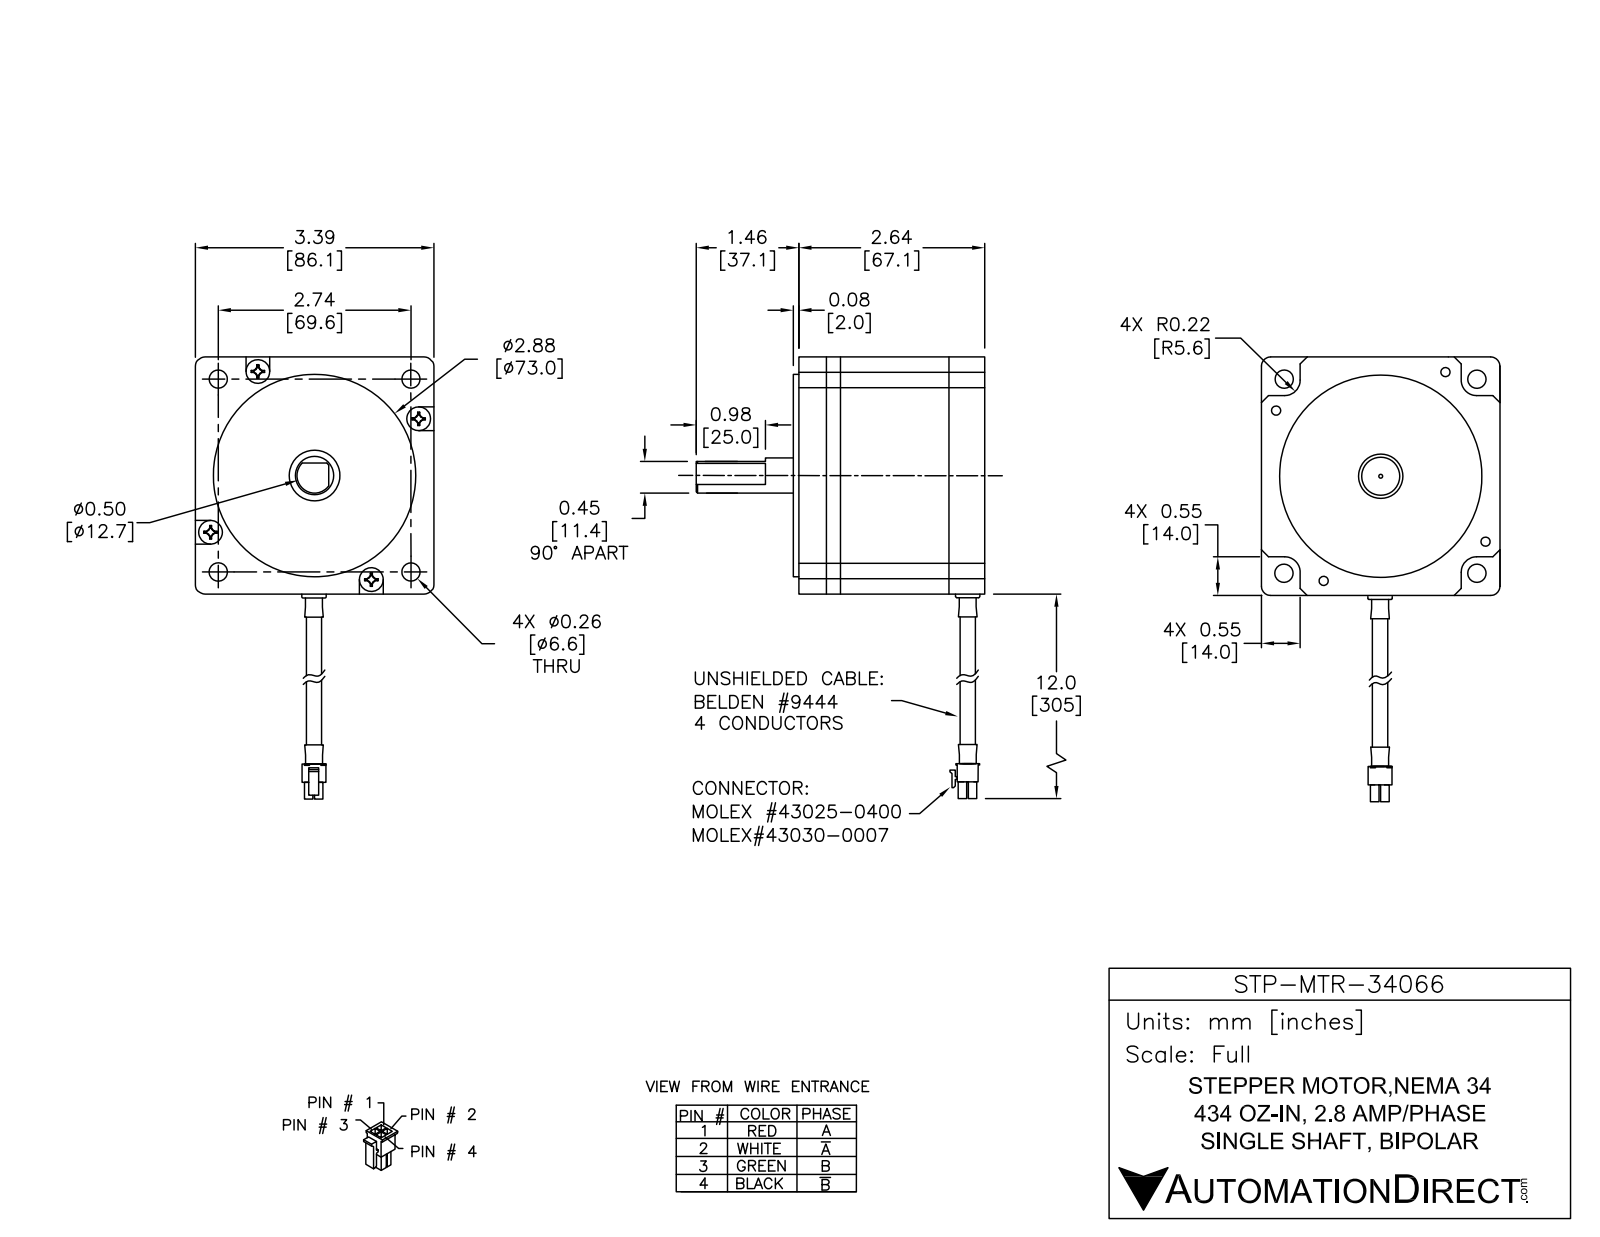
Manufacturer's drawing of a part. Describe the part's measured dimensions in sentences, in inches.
The part is named "STP-MTR-34066". Its 3-D file was written by "SolidWorks 2014 (AUTOMOTIVE_DESIGN)". It is 1 solid with 67 faces: 28 planar, 36 cylindrical and 3 other. Overall it measures 6.185 by 4.06 by 3.37 inches. Its volume is 27.1 cubic inches and its surface area 61.46 square inches. Round holes: 4 of diameter 0.26. Round bosses or shafts: 4 of diameter 0.05, 1 of diameter 2.875, 1 of diameter 0.5. Partial cylindrical surfaces (rounded edges, fillets, slot ends): 8 of radius 0.1, 1 of radius 1.94. The main face-to-face distances are 3.37, 0.574, 2.796, 2.66, 2.6, 0.06, 2.222, 0.4, 0.46, 2.2. The hole center spacings are 2.74, 3.875.
